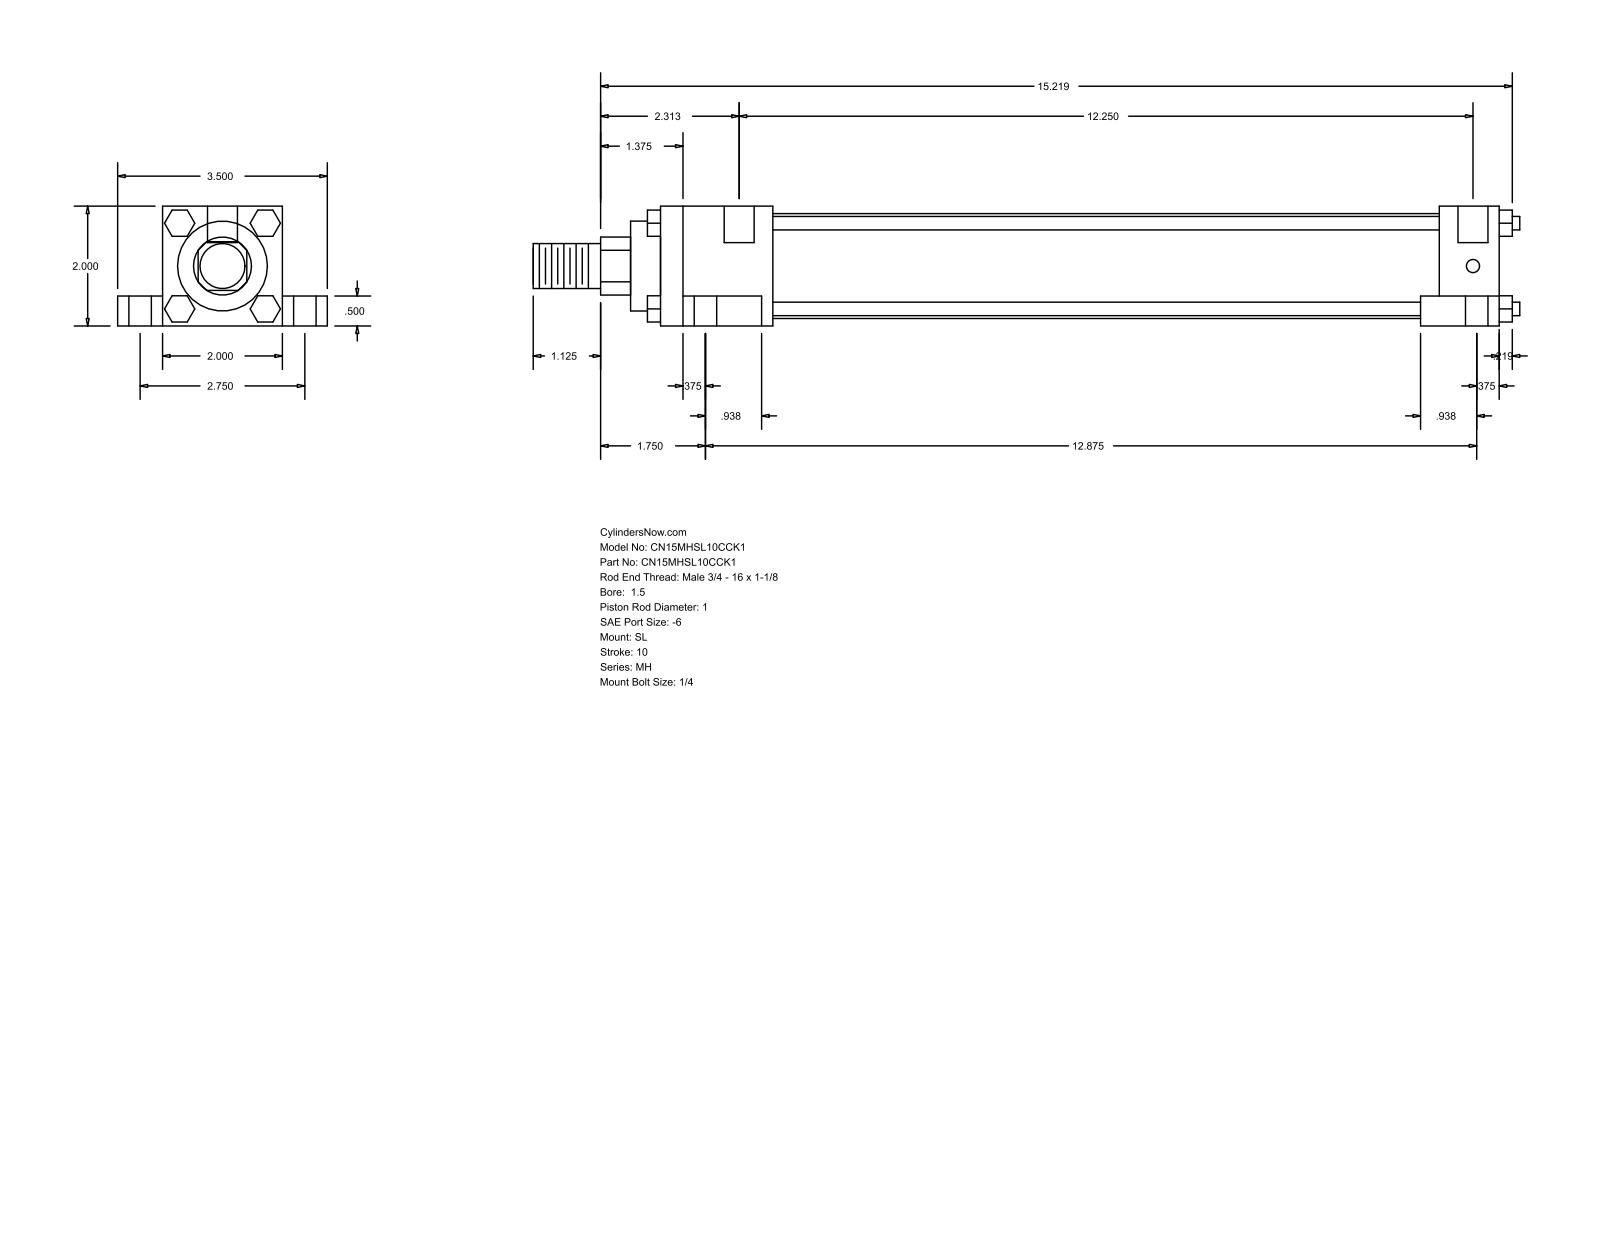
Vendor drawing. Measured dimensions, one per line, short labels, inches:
name: MH_SL__0150_1
written by: GSSL Pune (CONFIG_CONTROL_DESIGN)
unit: in
bodies: 0 solids, 148 faces (112 planar, 36 cylindrical, 0 other)
size: 16.469 × 3.5 × 2
holes: 4× ⌀0.219, 4× ⌀0.375, 4× ⌀0.625, 2× ⌀0.5
bosses: 4× ⌀0.225, 1× ⌀1.75, 1× ⌀1.5, 1× ⌀1, 1× ⌀0.75
rounds: 1× R0.484
face distances: 2, 0.5, 1.5, 0.75, 2.75, 14, 1, 0.375, 1.313, 12.313
hole spacings: 1.376, 1.443, 1.485, 2.75, 12.375, 12.389, 12.513, 12.875
